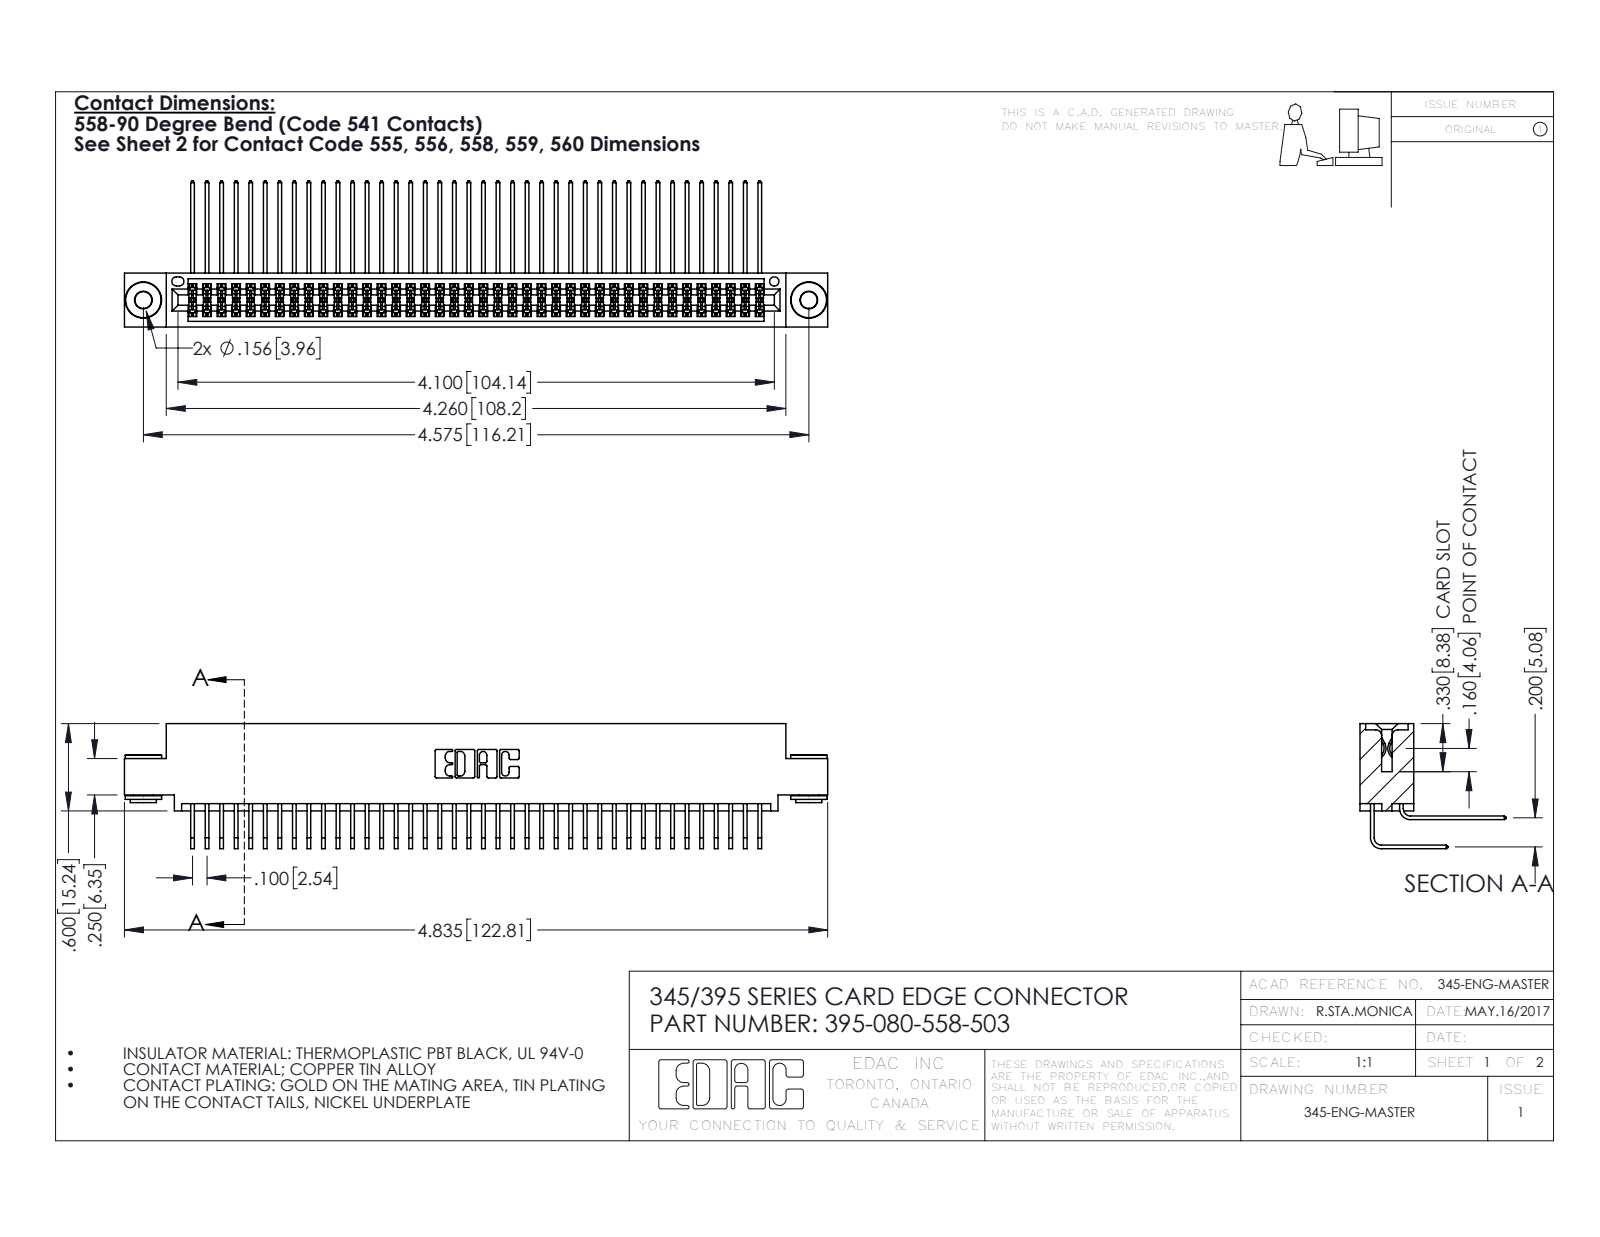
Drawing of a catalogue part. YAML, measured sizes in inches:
part_name: "345 Part_0.110 Offset - 0.156 Dia-TH; 395-080-558-503; 345-292-001_558 Tail - 2; 345-250-002_345-250-002-102 (+1 more)"
step_written_by: "SolidWorks 2016 (CONFIG_CONTROL_DESIGN)"
units: inches
bodies: {solids: 83, faces: 4328, planar: 2894, cylindrical: 1426, other: 8}
overall_size: [4.835, 1.005, 0.859]
volume: 0.752
surface_area: 31.99
round_holes:
  - {diameter: 0.116, count: 2}
  - {diameter: 0.156, count: 2}
  - {diameter: 0.064, count: 1}
round_bosses_or_shafts:
  - {diameter: 0.25, count: 2}
  - {diameter: 0.18, count: 2}
  - {diameter: 0.136, count: 2}
partial_cylinders:
  - {radius: 0.006, count: 121}
  - {radius: 0.01, count: 22}
  - {radius: 0.007, count: 6}
  - {radius: 0.031, count: 6}
  - {radius: 0.026, count: 3}
  - {radius: 0.014, count: 2}
  - {radius: 0.019, count: 2}
  - {radius: 0.022, count: 2}
face_to_face_distances: [0.072, 0.298, 0.2, 0.37, 0.025, 0.098, 0.272, 0.225, 0.025, 0.175]
hole_center_spacings: [0.27, 4.339, 4.575]
